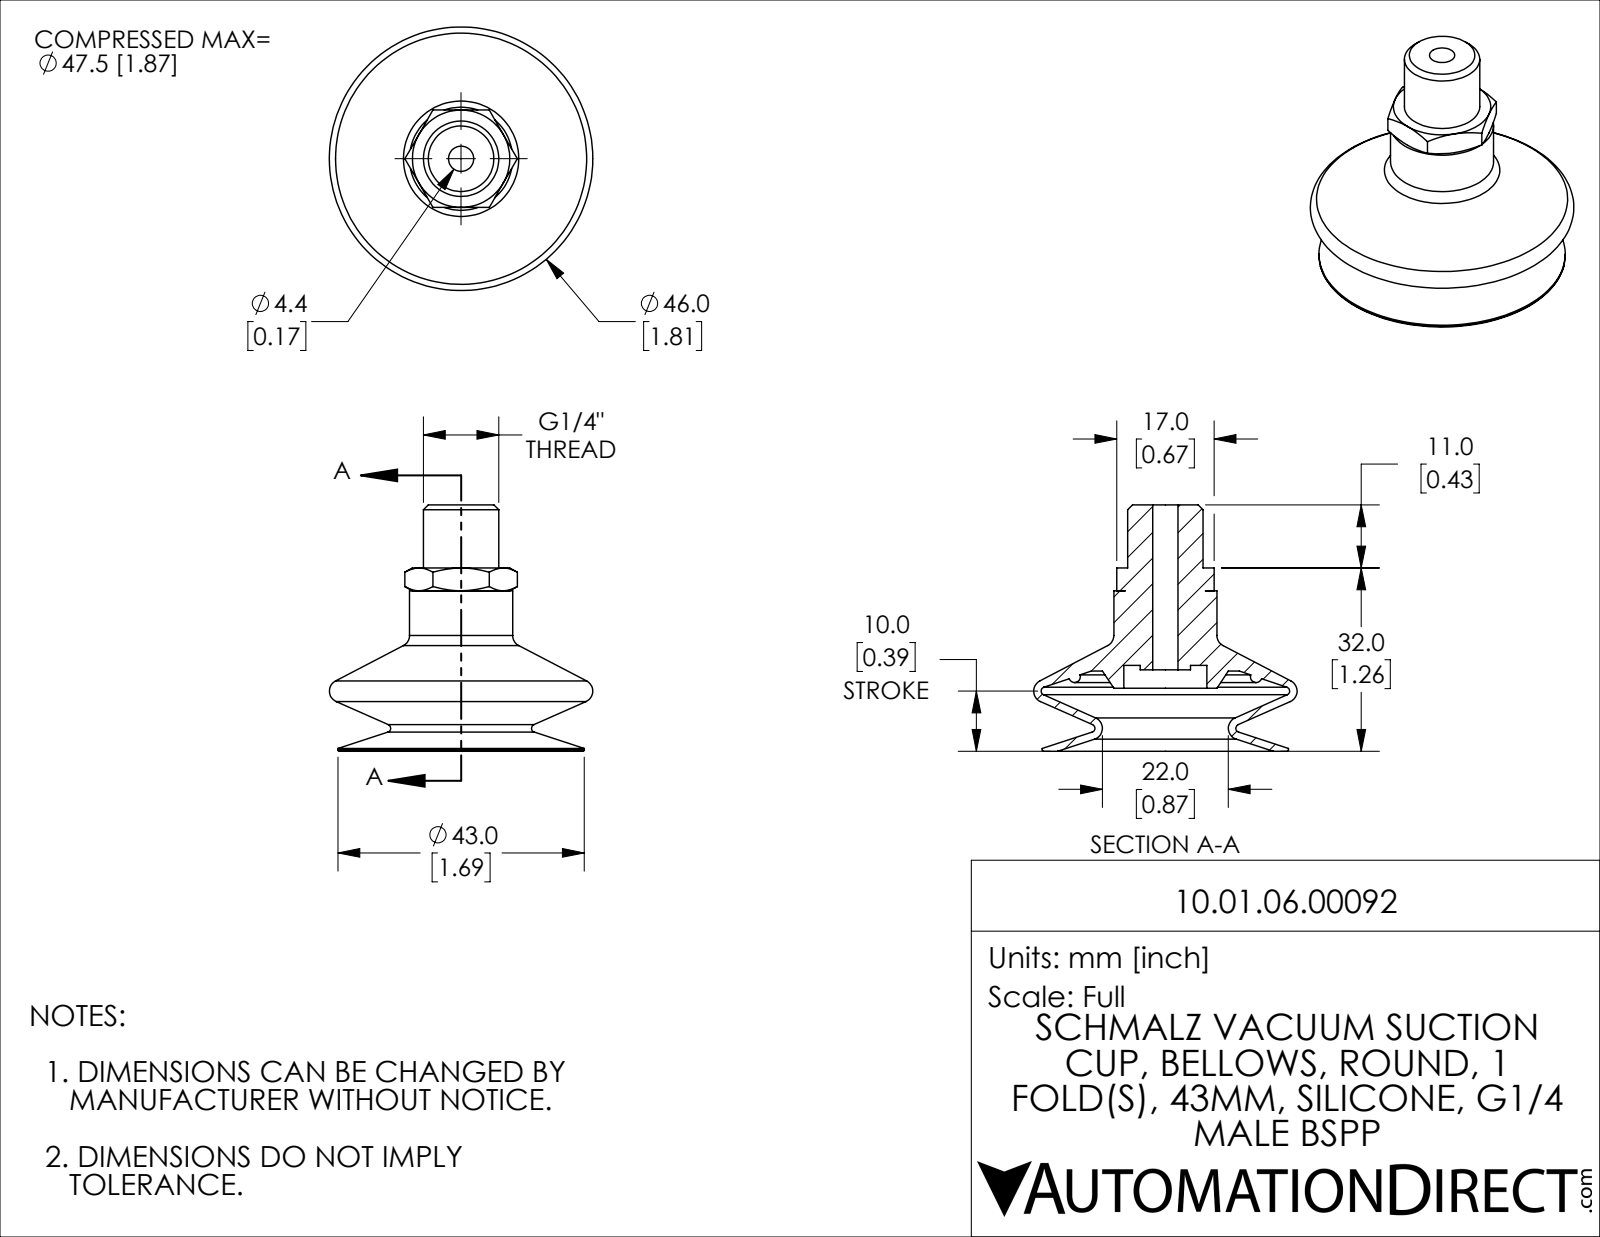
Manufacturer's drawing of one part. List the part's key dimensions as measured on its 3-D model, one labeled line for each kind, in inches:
Part name (STEP PRODUCT): 10.01.06.00092
STEP written by: SolidWorks 2021 (CONFIG_CONTROL_DESIGN)
Units: inches
Bodies: 1 solid, 79 faces (15 planar, 12 cylindrical, 52 other)
Overall size (bounding box): 1.811 × 1.811 × 1.693
Volume: 0.766 in³ · Surface area: 16.68 in²
Round holes (diameter × count): ⌀0.173 ×1, ⌀0.571 ×1
Round bosses / shafts (diameter × count): ⌀1.693 ×1, ⌀0.709 ×1, ⌀0.518 ×1, ⌀0.346 ×1
Main face-to-face distances: 0.551, 0.669, 1.102, 0.591, 0.157, 1.26, 0.433, 0.039, 0.512, 0.709
